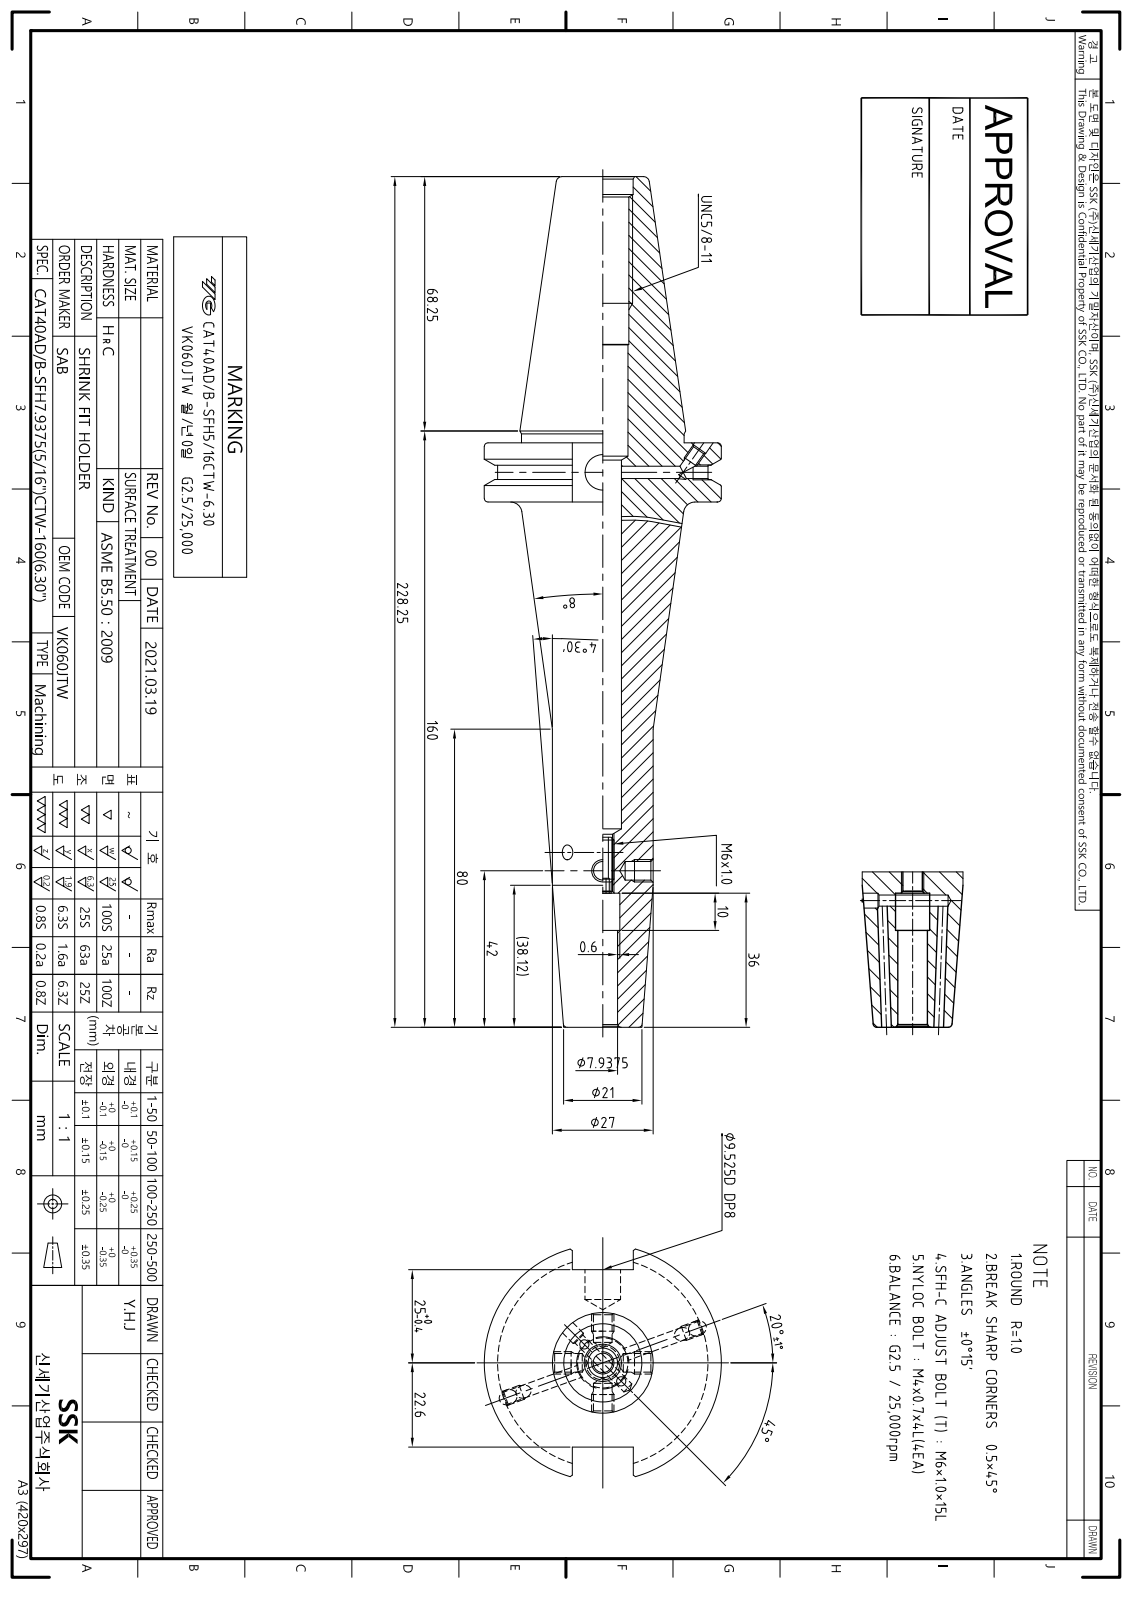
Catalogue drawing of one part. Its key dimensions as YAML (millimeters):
part_name: "LO-CAT40ADB-SFH7.9375CTW-160"
step_written_by: "Autodesk Inventor 2024 (AUTOMOTIVE_DESIGN)"
units: millimeters
bodies: {solids: 1, faces: 94, planar: 39, cylindrical: 32, other: 23}
overall_size: [228.25, 63.5, 61.09]
volume: 194922
surface_area: 37365
round_holes:
  - {diameter: 3.24, count: 4}
  - {diameter: 2.5, count: 2}
  - {diameter: 4, count: 2}
  - {diameter: 4.2, count: 2}
  - {diameter: 4.92, count: 1}
  - {diameter: 7.94, count: 1}
  - {diameter: 9.14, count: 1}
  - {diameter: 9.53, count: 1}
  - {diameter: 10, count: 1}
  - {diameter: 13, count: 1}
  - {diameter: 13.39, count: 1}
  - {diameter: 16.3, count: 1}
round_bosses_or_shafts:
  - {diameter: 63.5, count: 1}
  - {diameter: 43.6, count: 1}
  - {diameter: 27, count: 1}
partial_cylinders:
  - {radius: 28.15, count: 1}
face_to_face_distances: [15.88, 156.83, 140.95, 47.6, 16.38, 71.42, 87.3, 228.25, 77.47, 6.05]
